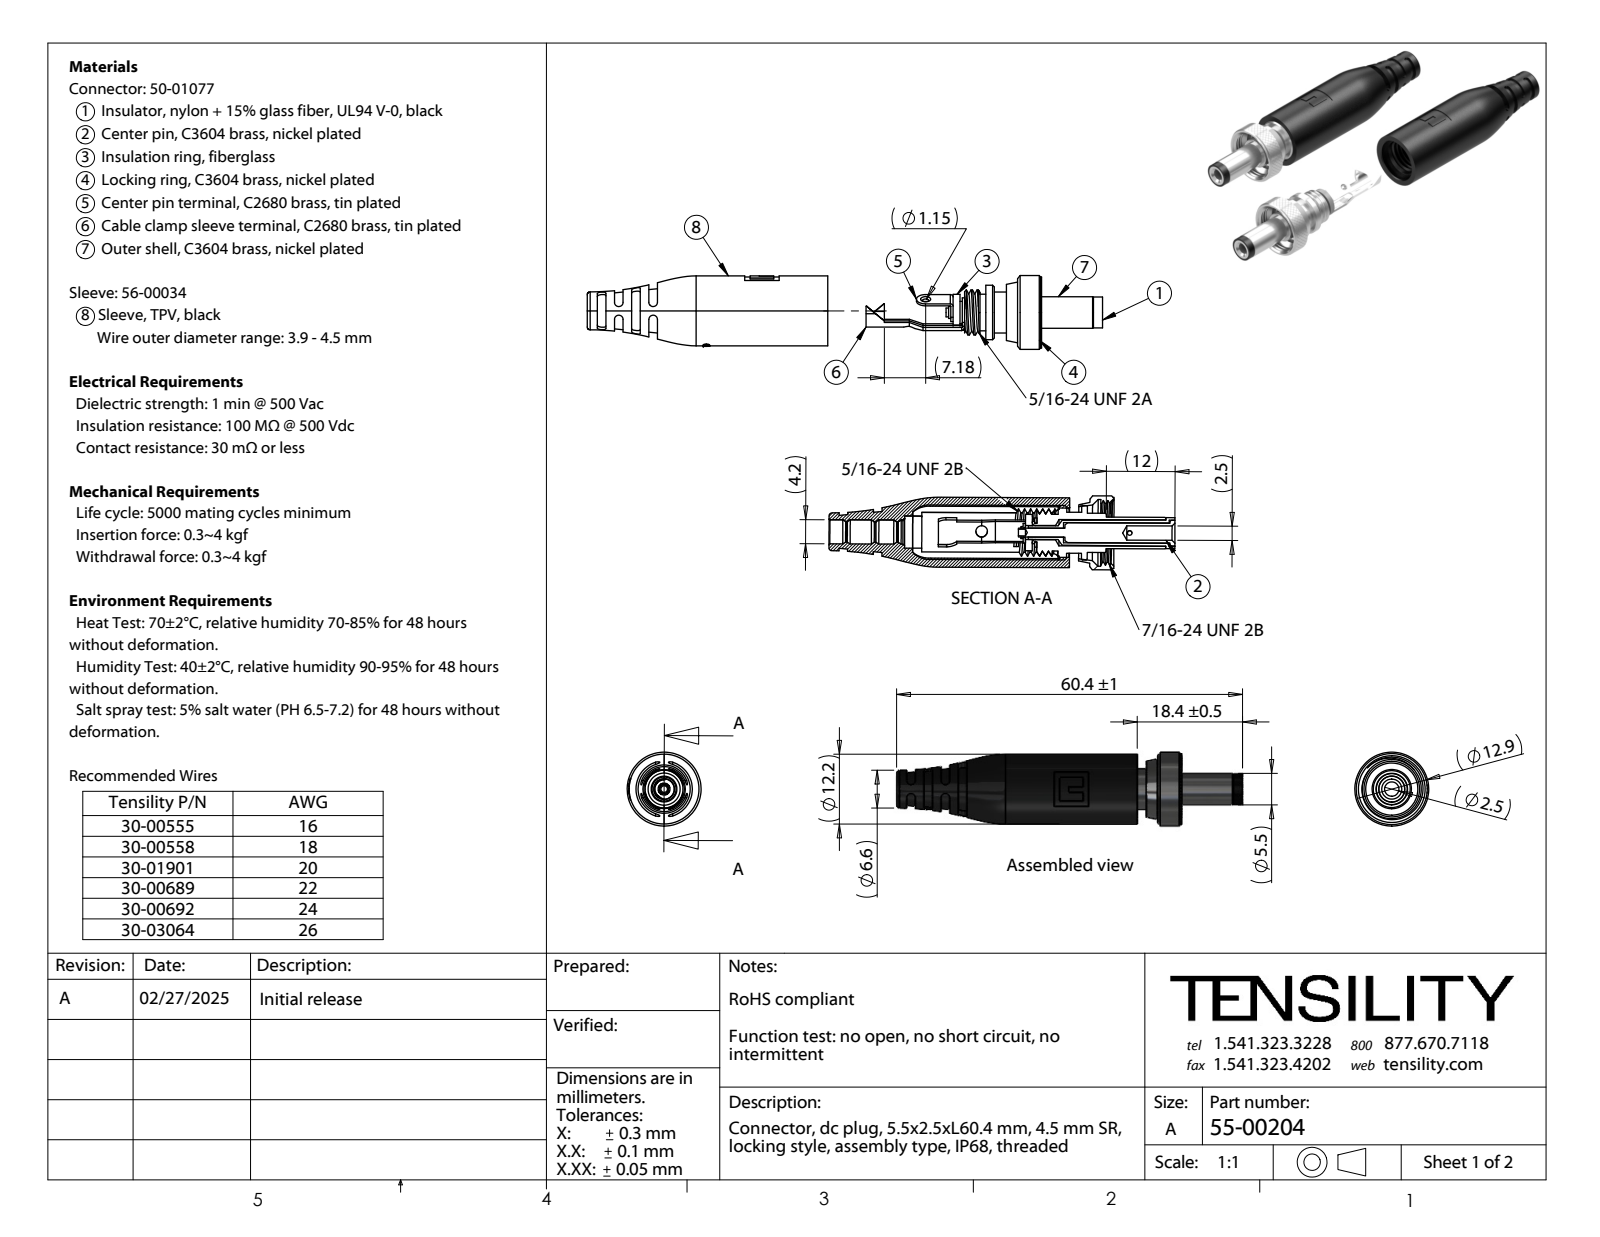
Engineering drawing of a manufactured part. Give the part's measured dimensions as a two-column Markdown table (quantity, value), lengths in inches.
| quantity | value |
| --- | --- |
| part name | 50-01077_Floating locking ring_Step; 56-00034; 55-00204; 50-01077_Cable clamp sleeve terminal (+8 more) |
| STEP written by | SolidWorks 2021 (CONFIG_CONTROL_DESIGN) |
| units | inches |
| bodies | 11 solids, 580 faces (193 planar, 196 cylindrical, 191 other) |
| overall size | 2.404 × 0.508 × 0.508 |
| volume | 0.361 in³ |
| surface area | 17.47 in² |
| round holes (diameter × count) | 0.045 × 2, 0.031 × 1, 0.063 × 1, 0.079 × 1, 0.096 × 1, 0.098 × 1, 0.132 × 1, 0.14 × 1, 0.179 × 1, 0.181 × 1, 0.22 × 1, 0.272 × 1 |
| round bosses / shafts (diameter × count) | 0.508 × 1, 0.488 × 1, 0.48 × 1, 0.309 × 1, 0.281 × 1, 0.27 × 1, 0.252 × 1, 0.217 × 1 |
| partial cylindrical surfaces (radius × count) | 0.03 × 16, 0.008 × 4, 0.062 × 2, 0.24 × 2, 0.004 × 1, 0.016 × 1, 0.02 × 1, 0.024 × 1 |
| main face-to-face distances | 0.059, 0.067, 1.171, 1.177, 0.161, 0.053, 0.132, 0.016, 0.169, 1.104 |
